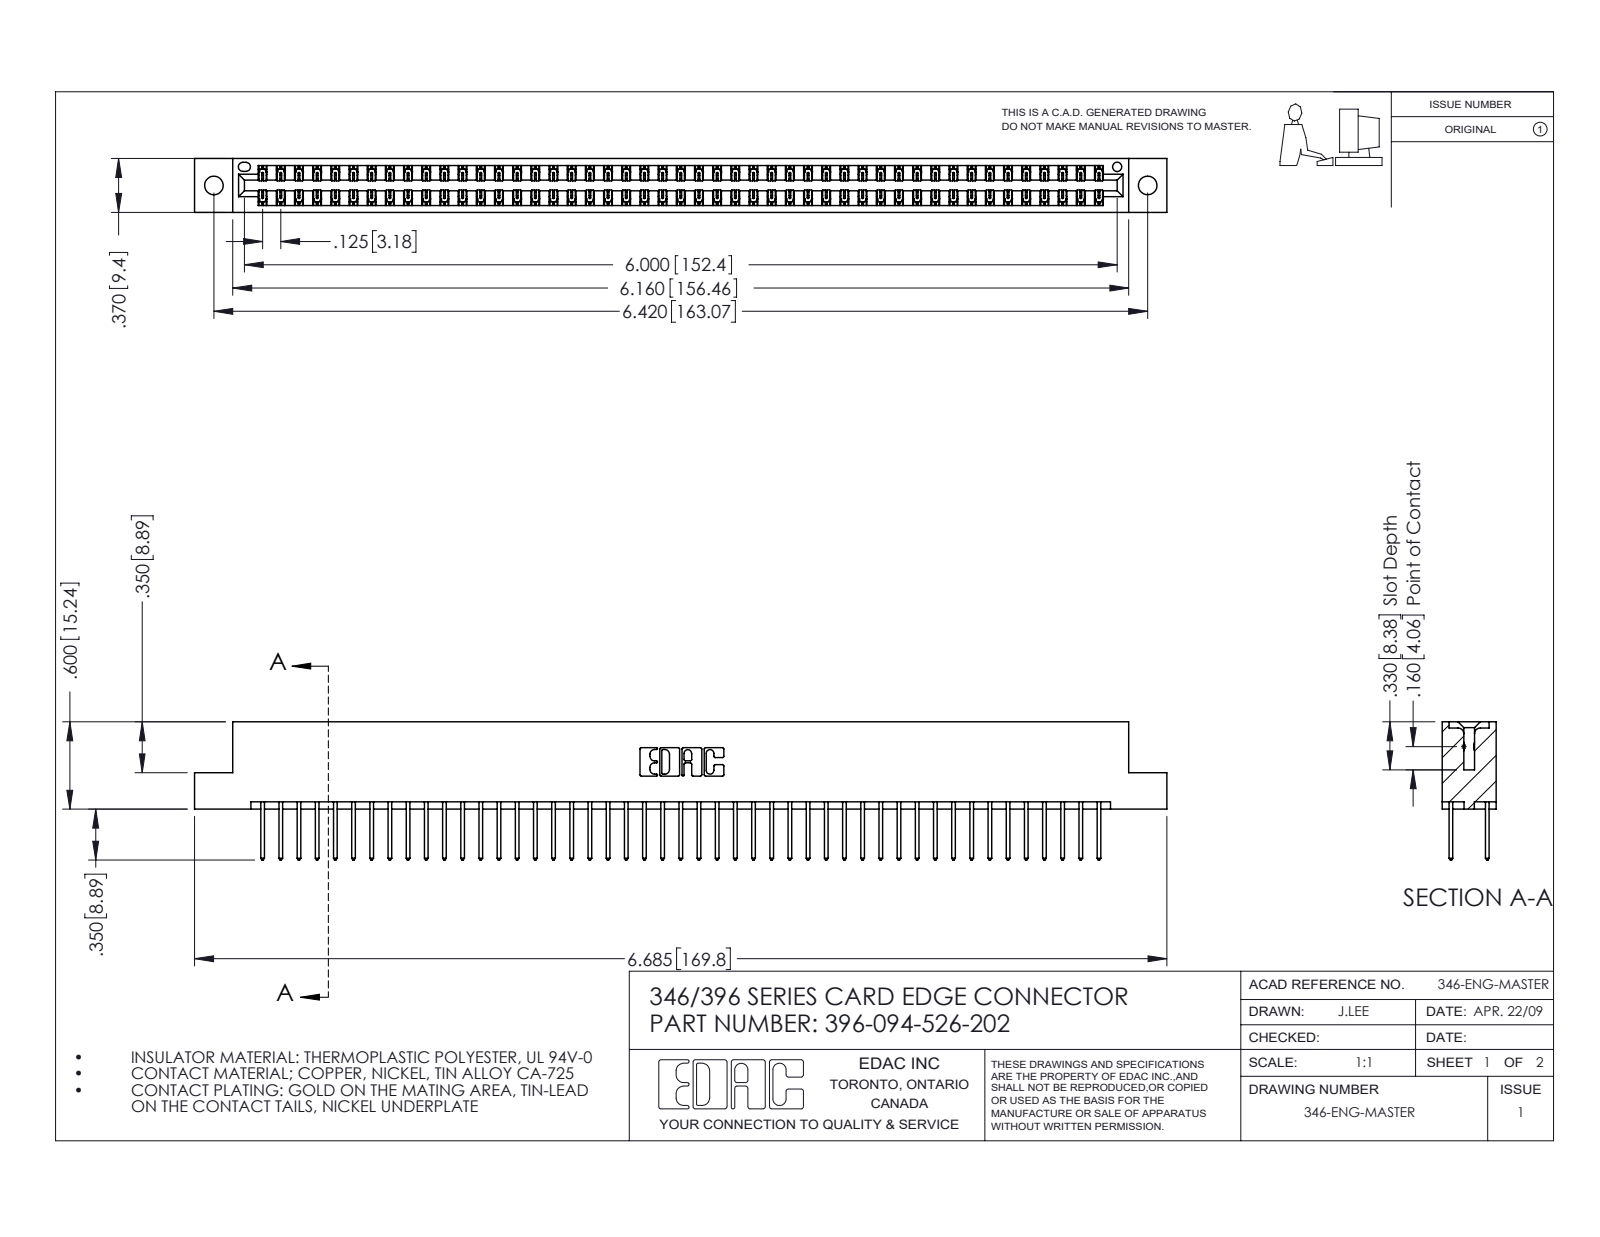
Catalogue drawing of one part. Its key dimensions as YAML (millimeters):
part_name: "345-292-001_345-293-126; 396-094-526-202; 346 Part_Flush Mounting Lugs - 0.128 Dia"
step_written_by: "SolidWorks 2016 (CONFIG_CONTROL_DESIGN)"
units: millimeters
bodies: {solids: 95, faces: 5010, planar: 3366, cylindrical: 1644, other: 0}
overall_size: [169.8, 24.1, 9.4]
volume: 16710
surface_area: 23470
round_holes:
  - {diameter: 3.3, count: 2}
  - {diameter: 1.6, count: 1}
partial_cylinders:
  - {radius: 0.2, count: 141}
  - {radius: 0.3, count: 94}
  - {radius: 0.3, count: 22}
  - {radius: 0.2, count: 6}
  - {radius: 0.8, count: 6}
  - {radius: 0.7, count: 3}
  - {radius: 0.4, count: 2}
  - {radius: 0.6, count: 2}
face_to_face_distances: [1.2, 8.2, 6.4, 9.4, 1.8, 7.6, 0.6, 7, 3.8, 5.6]
hole_center_spacings: [6.2, 157.8, 163.1]
